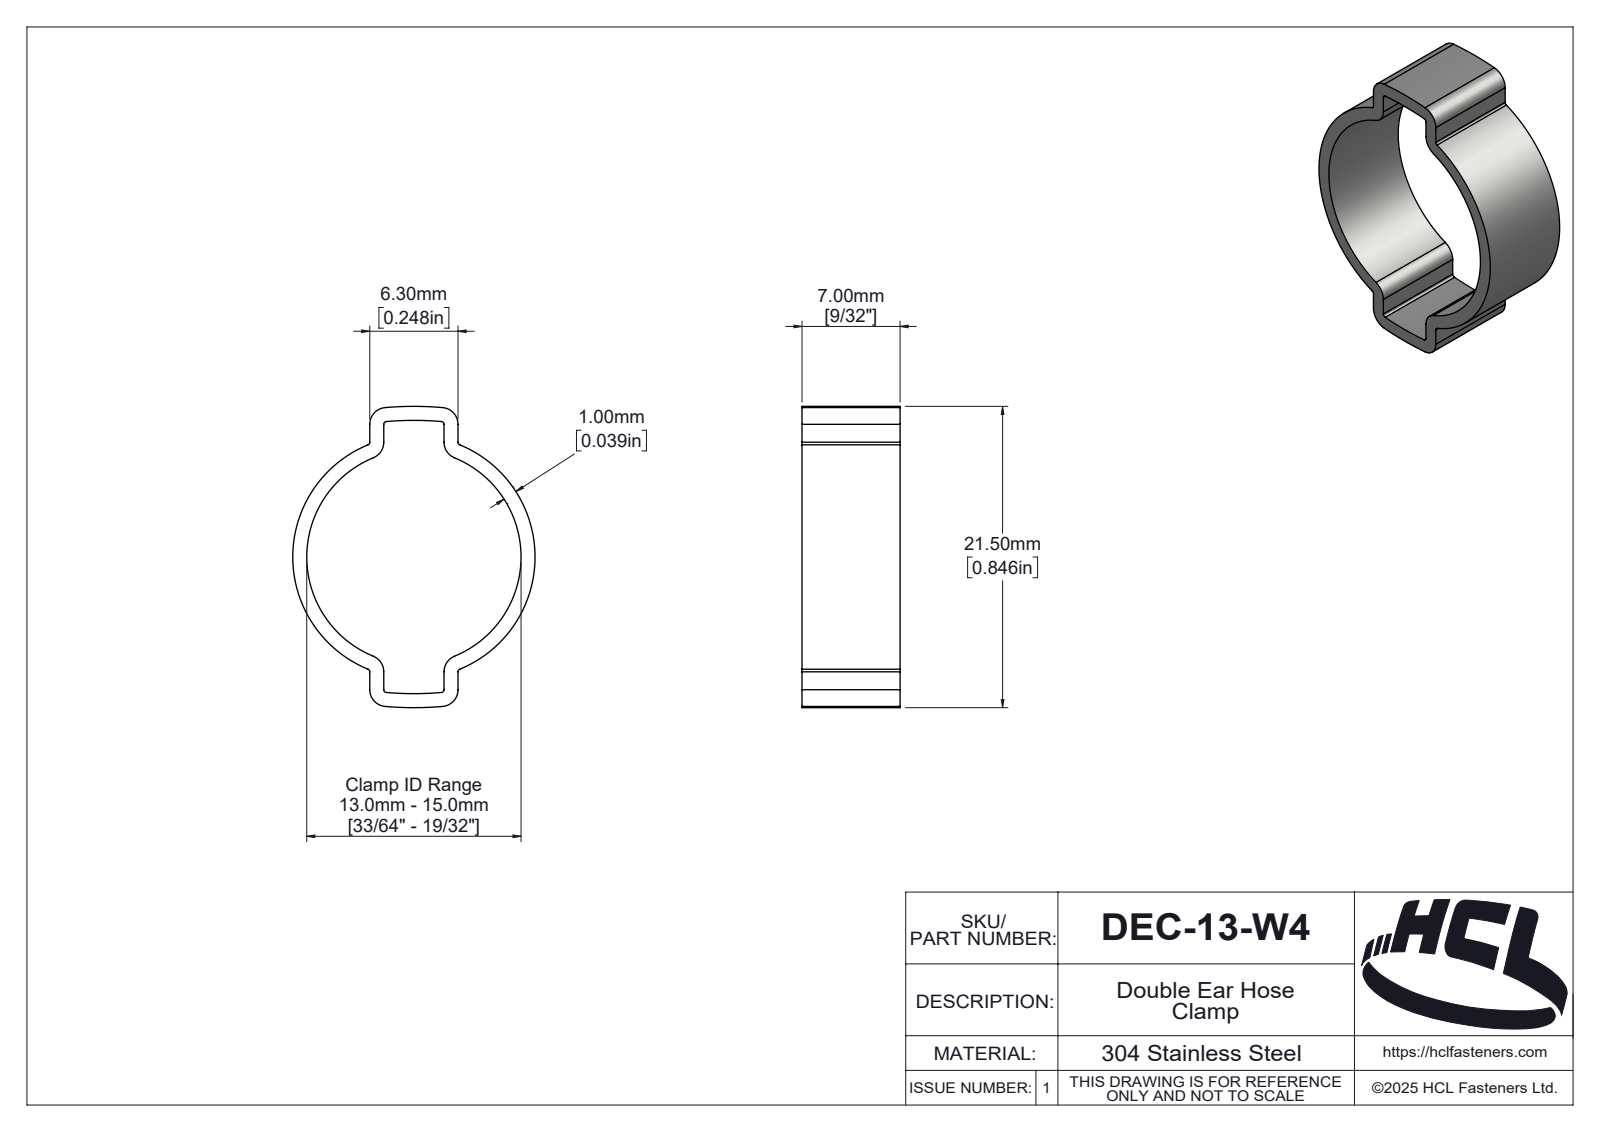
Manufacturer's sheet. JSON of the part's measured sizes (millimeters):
{"part_name": "DEC-13-W4", "step_written_by": "SolidWorks 2025 (AUTOMOTIVE_DESIGN)", "units": "millimeters", "bodies": {"solids": 1, "faces": 137, "planar": 12, "cylindrical": 76, "other": 49}, "overall_size": [21.5, 17.3, 7], "volume_mm3": 414, "surface_area_mm2": 949, "partial_cylinders_radius": [[0.2, 8], [1.2, 8], [23.16, 2], [24.16, 2], [0.13, 1], [0.54, 1], [0.67, 1], [0.71, 1]], "face_to_face_distances": [7, 1, 5.3, 6.3, 4.3, 2.97, 1.97, 2.33, 3.33, 3.07]}
